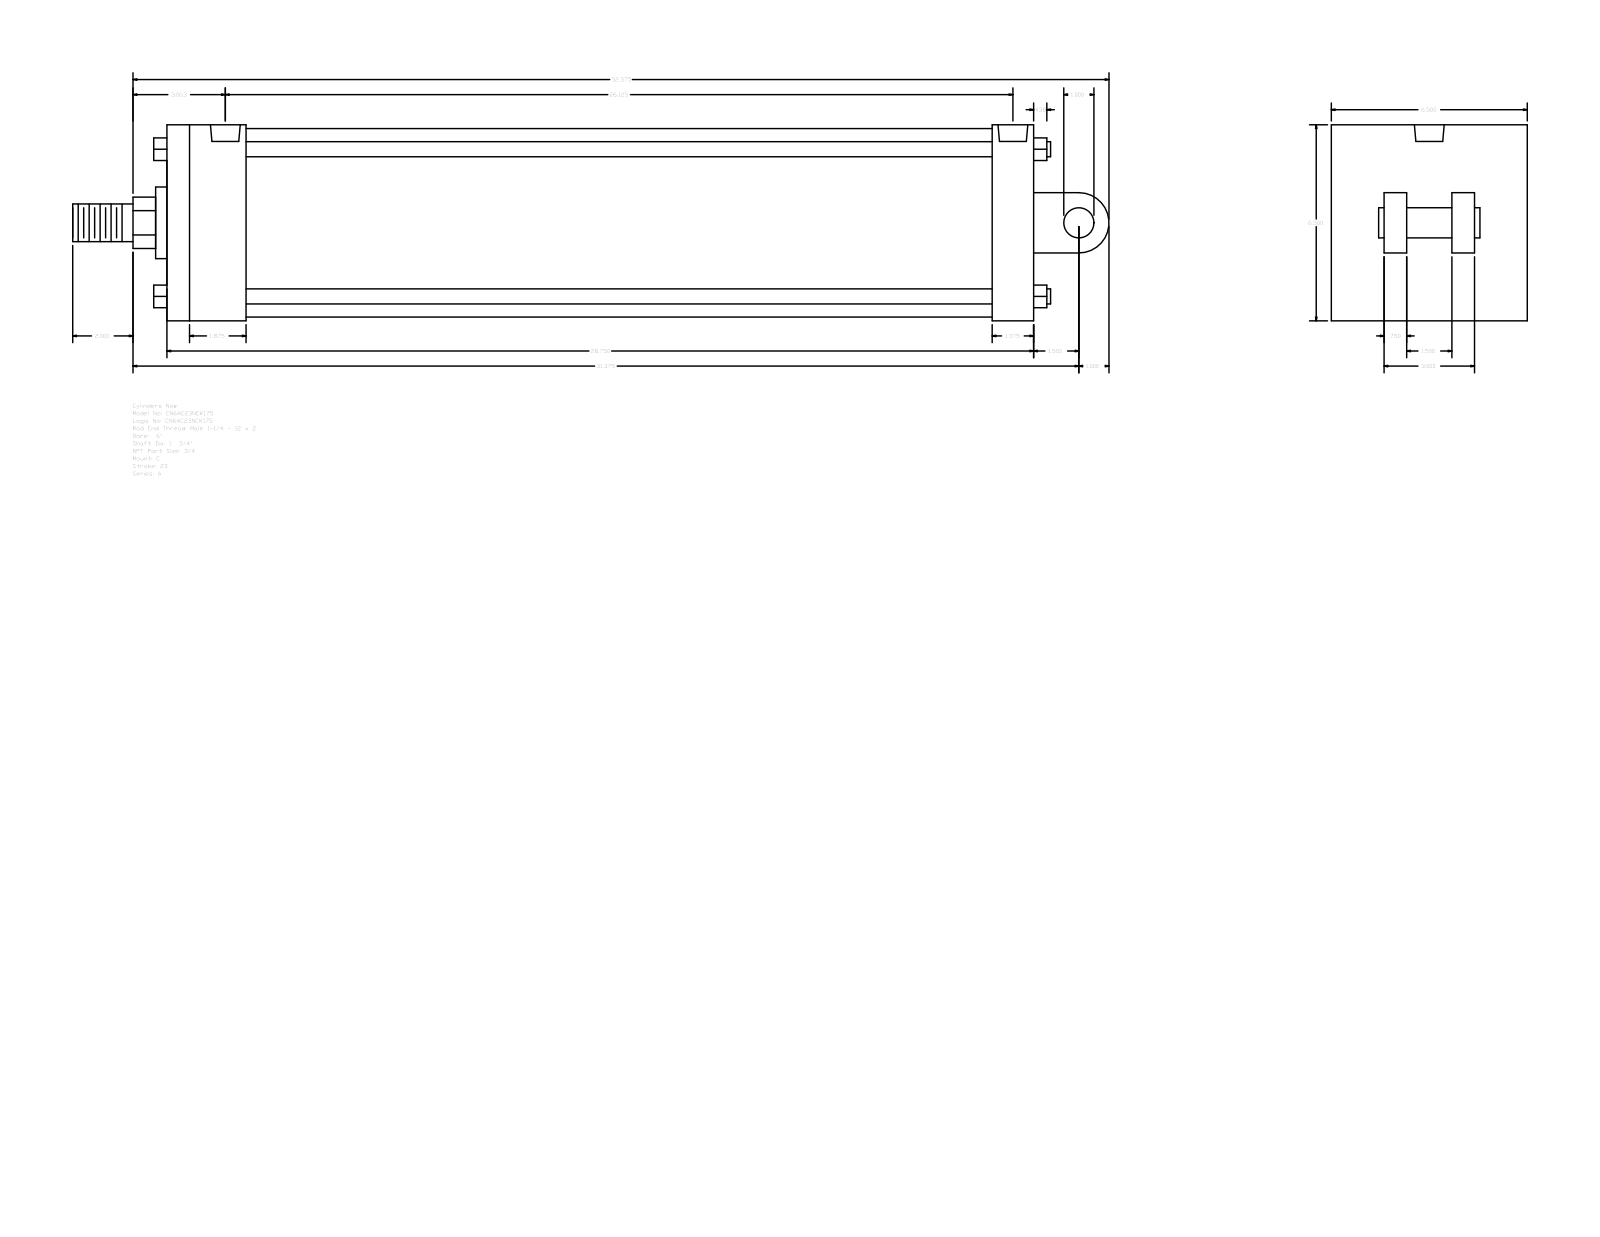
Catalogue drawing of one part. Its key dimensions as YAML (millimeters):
part_name: "A_C__0600_1.75"
step_written_by: "GSSL Pune (CONFIG_CONTROL_DESIGN)"
units: millimeters
bodies: {solids: 0, faces: 135, planar: 102, cylindrical: 33, other: 0}
overall_size: [873.12, 165.1, 165.1]
round_holes:
  - {diameter: 15.08, count: 4}
  - {diameter: 25.12, count: 2}
round_bosses_or_shafts:
  - {diameter: 12.7, count: 4}
  - {diameter: 158.75, count: 1}
  - {diameter: 60.33, count: 1}
  - {diameter: 44.45, count: 1}
  - {diameter: 31.75, count: 1}
  - {diameter: 25.4, count: 1}
partial_cylinders:
  - {radius: 21.63, count: 1}
  - {radius: 25.4, count: 1}
face_to_face_distances: [165.1, 730.26, 19.05, 57.15, 66.68, 663.58, 695.33, 628.65, 34.93, 63.5]
hole_center_spacings: [5.56, 652.45, 658.01, 663.57]
